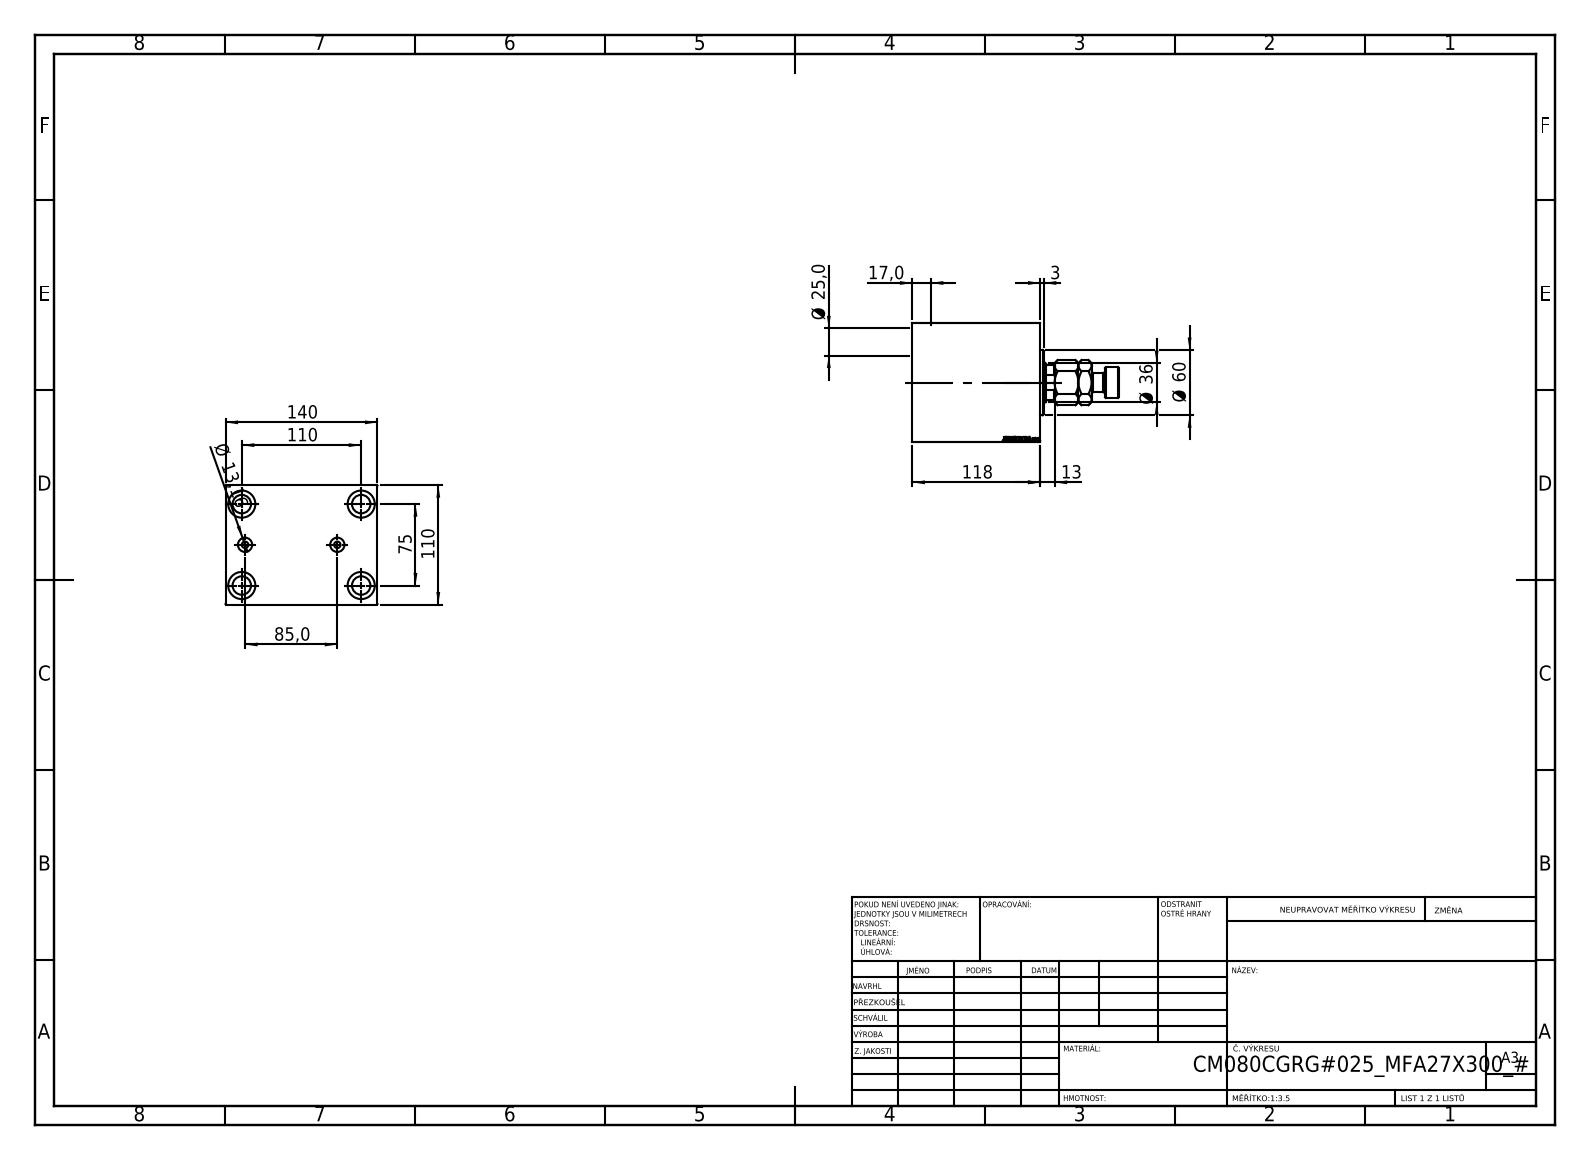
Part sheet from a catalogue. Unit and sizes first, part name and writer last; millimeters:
Units: millimetres
Overall size (bounding box): 190 × 140 × 110
Round holes (diameter × count): ⌀17 ×4, ⌀25 ×4, ⌀6 ×2, ⌀13.16 ×2, ⌀25.5 ×1, ⌀36 ×1, ⌀39.5 ×1, ⌀80 ×1, ⌀82 ×1, ⌀87 ×1
Round bosses / shafts (diameter × count): ⌀60 ×1, ⌀28 ×1, ⌀18 ×1
Partial cylindrical surfaces — rounded edges, fillets, slot ends (radius × count): R17.5 ×1
Main face-to-face distances: 110, 140, 118, 67, 51, 10, 21.6, 29.4, 96.4, 86.4
Hole centre spacings: 66.57, 37.62, 43.48, 75, 95.66, 110, 113.38, 133.14
Volume: 1 675 000 mm³ · Surface area: 183 353 mm²
Bodies: 4 solids, 912 faces (424 planar, 62 cylindrical, 426 other)
Part name (STEP PRODUCT): MFA; V450CM_C_Body; V450CM_VC_B; V450CM_C_VCP
STEP written by: SolidWorks 2019 (CONFIG_CONTROL_DESIGN)
